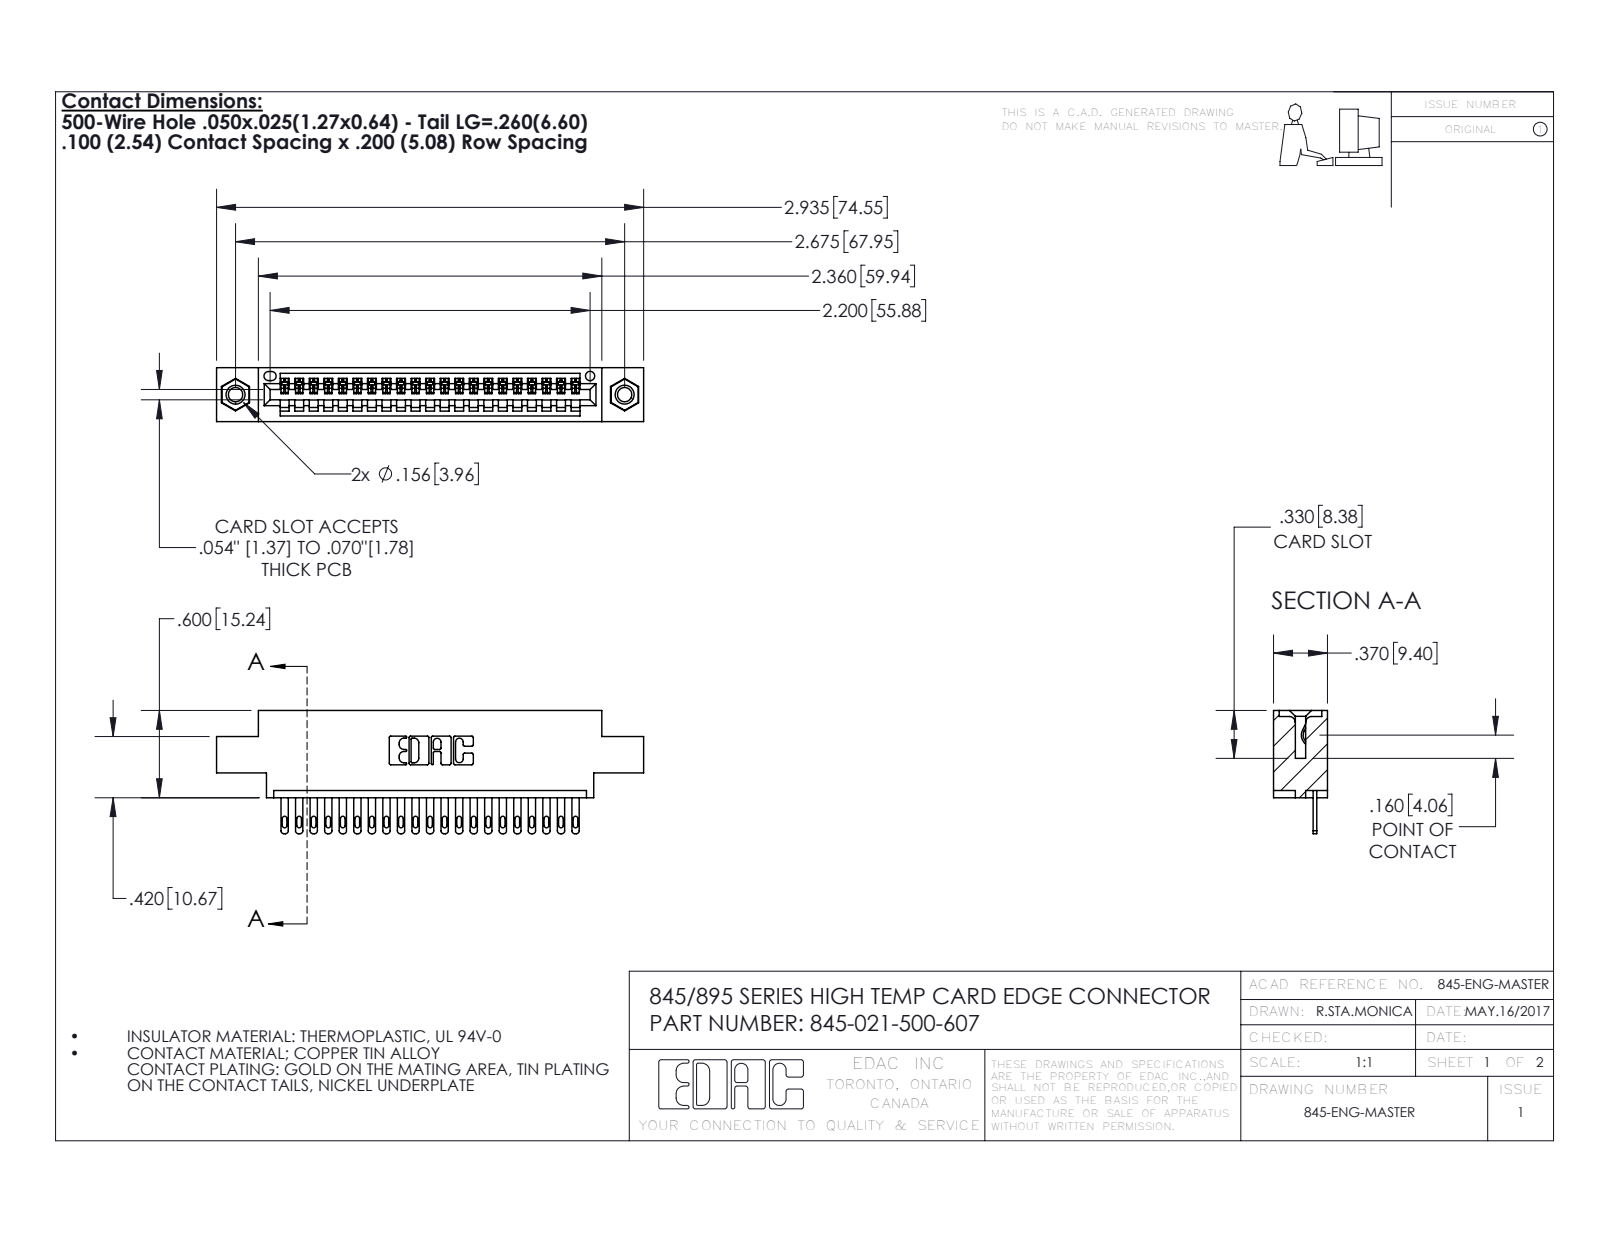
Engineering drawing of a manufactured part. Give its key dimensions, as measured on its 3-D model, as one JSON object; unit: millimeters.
{"part_name": "345-292-001_345-293-100; 345-250-001_345-250-005-103; 345-021-500-607; 345 Part_0.170 Offset - 0.156 Dia-TI", "step_written_by": "SolidWorks 2016 (CONFIG_CONTROL_DESIGN)", "units": "millimeters", "bodies": {"solids": 24, "faces": 1324, "planar": 830, "cylindrical": 478, "other": 16}, "overall_size": [74.5, 21.5, 9.4], "volume_mm3": 6800, "surface_area_mm2": 8948, "round_holes": [[2.5, 2], [3.2, 2], [4, 2], [1.6, 1]], "round_bosses_or_shafts": [[3.9, 2]], "partial_cylinders_radius": [[0.2, 42], [0.4, 42], [0.5, 42], [0.3, 22], [0.2, 6], [0.8, 6], [0.7, 3], [0.8, 2]], "face_to_face_distances": [1.8, 7.6, 9.4, 5.1, 2.5, 6.9, 0.6, 5.7, 4.4, 3.8], "hole_center_spacings": [6.9, 62, 67.9]}
